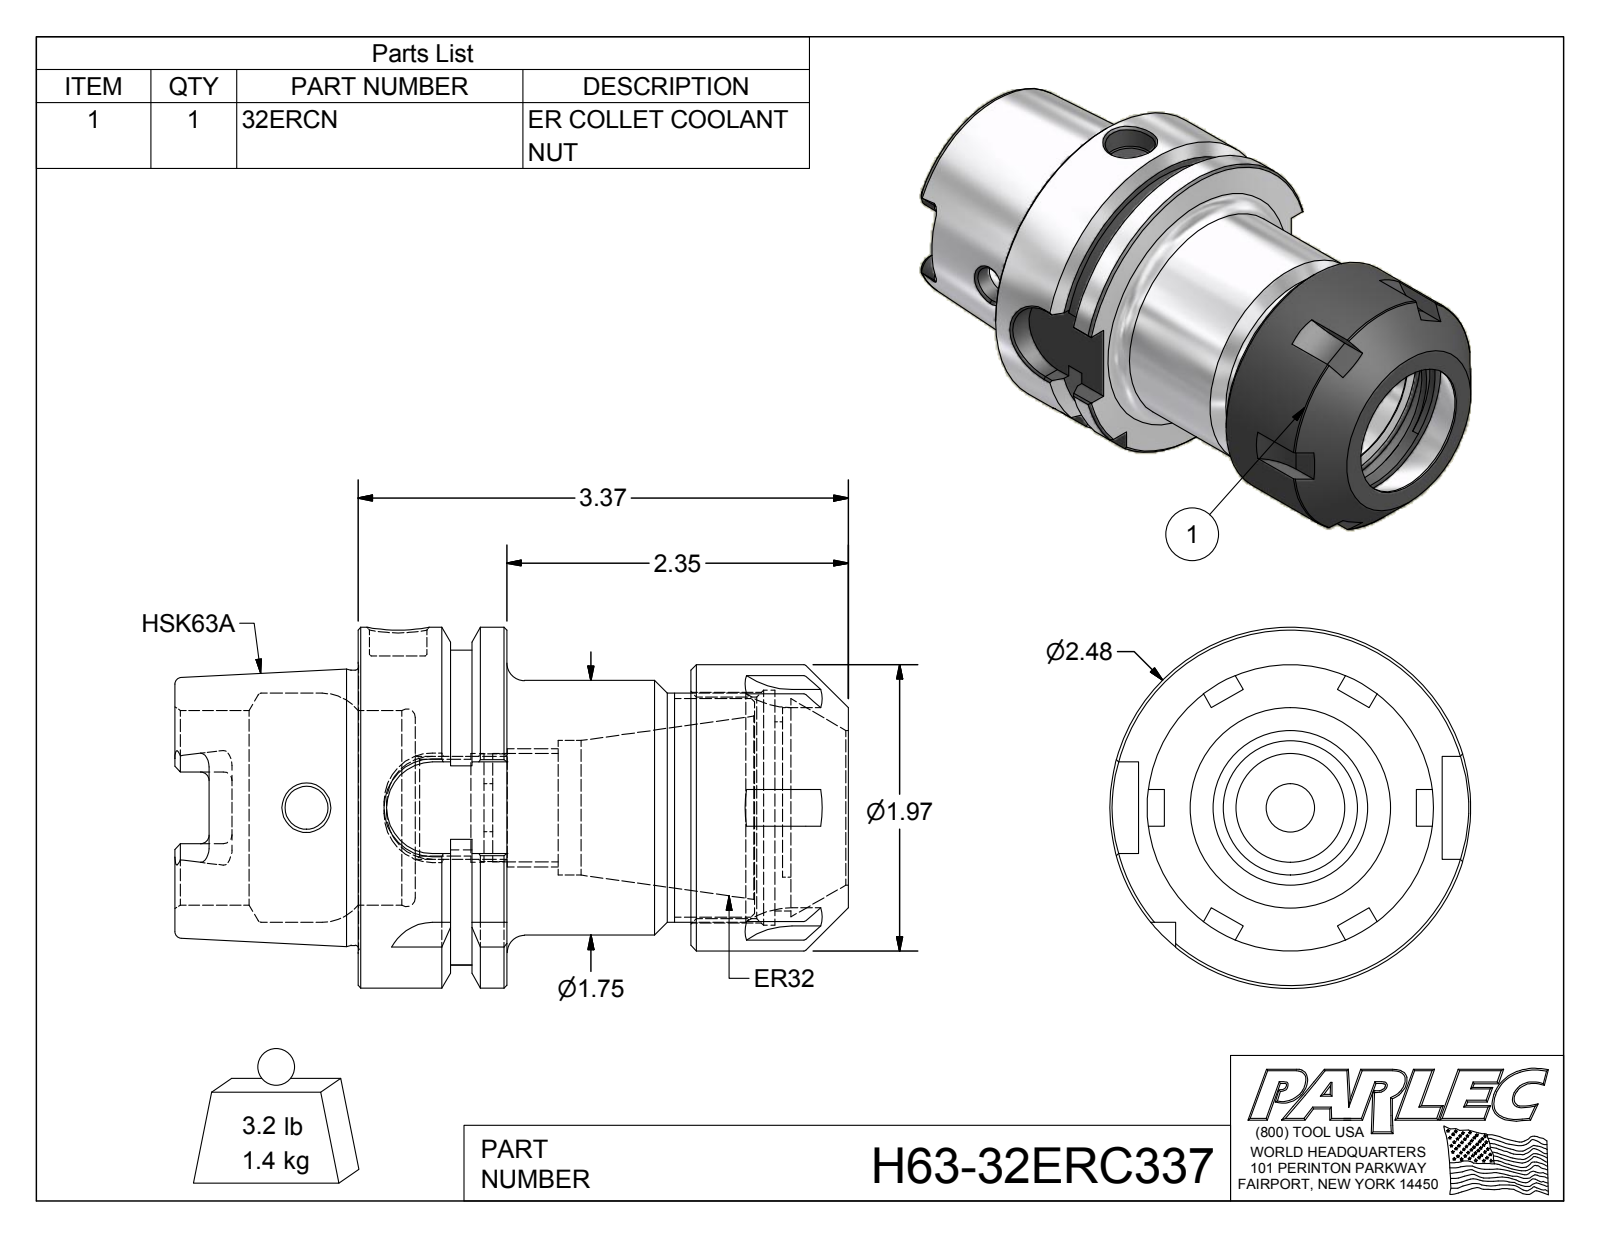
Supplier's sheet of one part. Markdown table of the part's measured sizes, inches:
| quantity | value |
| --- | --- |
| part name | H63-32ERC337; H63-32ER3-1; 32ERCN |
| STEP written by | Autodesk Inventor 2012 (AUTOMOTIVE_DESIGN) |
| units | inches |
| bodies | 2 solids, 184 faces (76 planar, 48 cylindrical, 60 other) |
| overall size | 4.63 × 2.48 × 2.48 |
| volume | 8.573 in³ |
| surface area | 63.52 in² |
| round holes (diameter × count) | 0.295 × 1, 0.331 × 1, 0.394 × 1, 0.666 × 1, 0.745 × 1, 0.749 × 1, 0.925 × 1, 1.063 × 1, 1.299 × 1, 1.339 × 1, 1.522 × 1, 1.575 × 1 |
| round bosses / shafts (diameter × count) | 2.48 × 1, 1.969 × 1, 1.891 × 1, 1.75 × 1 |
| partial cylindrical surfaces (radius × count) | 0.059 × 6, 0.5 × 6, 0.113 × 4, 0.315 × 4, 0.689 × 1, 1.083 × 1 |
| main face-to-face distances | 1.024, 0.241, 0.389, 0.394, 0.63, 2.287, 1.894, 1.264, 2.866, 2.472 |
| hole center spacings | 0.059 |
